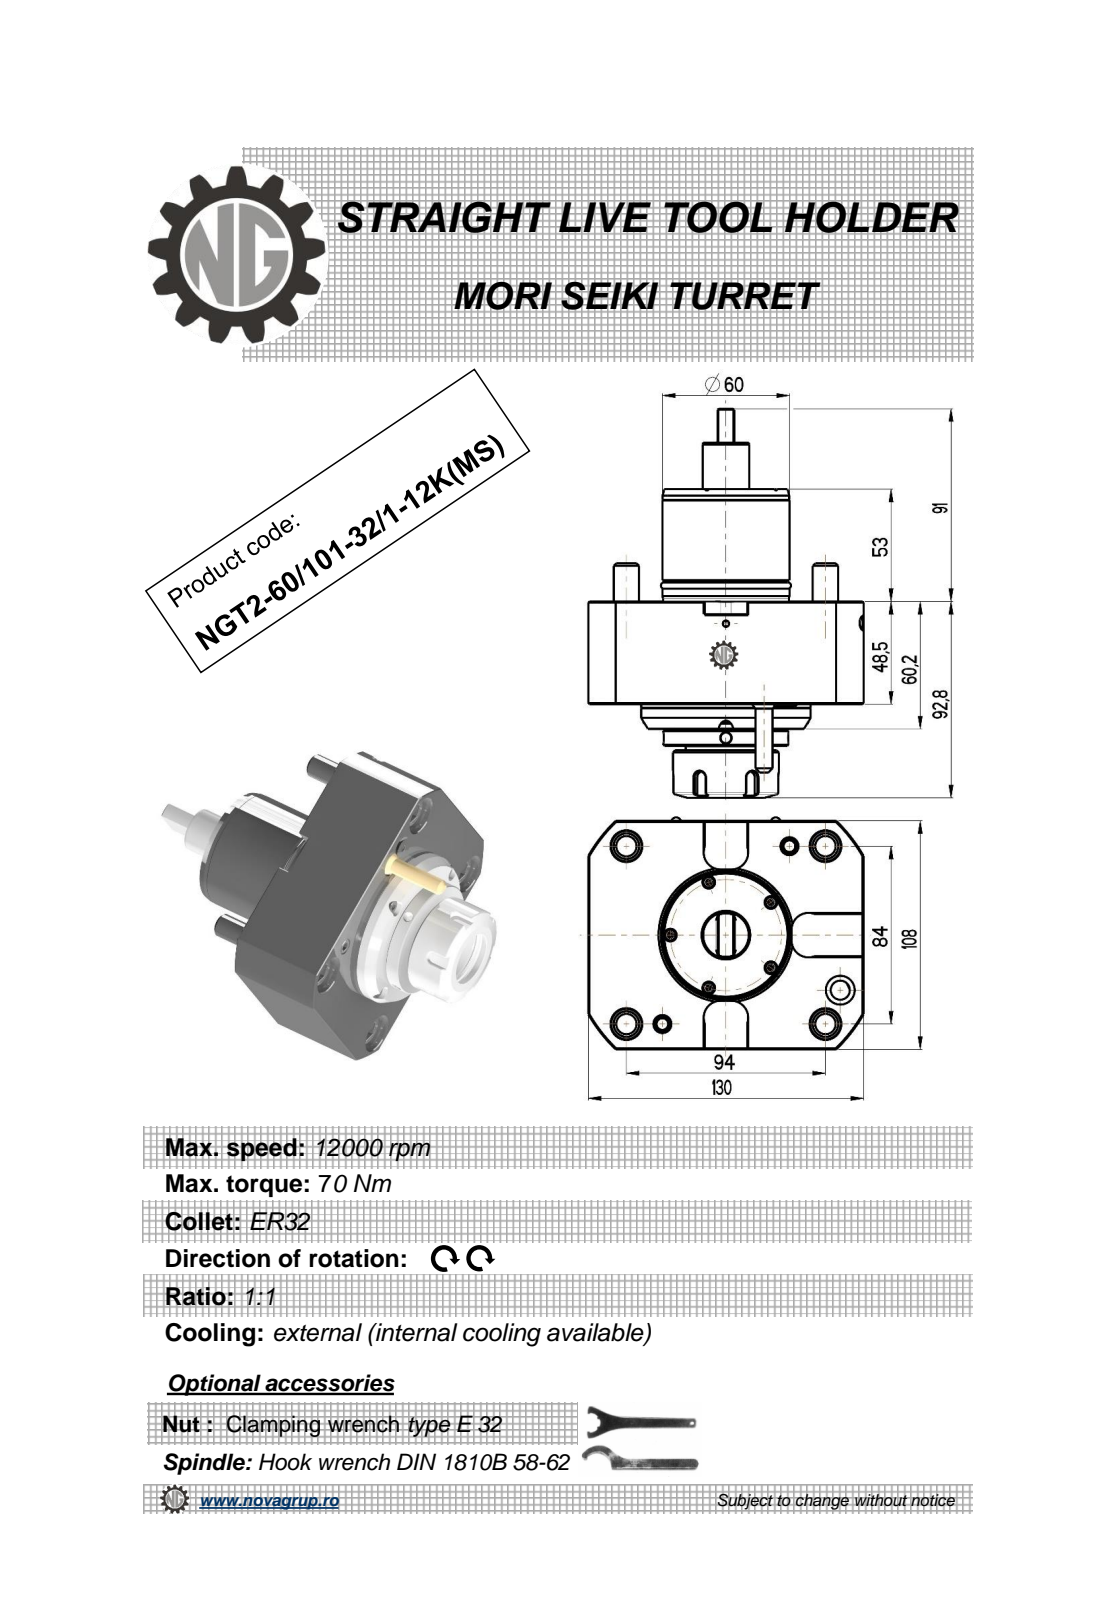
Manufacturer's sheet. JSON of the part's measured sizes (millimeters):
{"part_name": "NGT2_60_101_32_1_MS", "step_written_by": "PRO/ENGINEER BY PARAMETRIC TECHNOLOGY CORPORATION, 2010280 (CONFIG_CONTROL_DESIGN)", "units": "millimeters", "bodies": {"solids": 2, "faces": 267, "planar": 93, "cylindrical": 83, "other": 91}, "overall_size": [183.8, 130, 109.6], "volume_mm3": 934229, "surface_area_mm2": 78764, "round_holes": [[5, 3], [3, 1], [9, 1], [27, 1]], "round_bosses_or_shafts": [[12, 4], [80, 1], [60, 1], [59.8, 1], [59.4, 1], [55.4, 1], [50, 1], [48, 1]], "partial_cylinders_radius": [[0.22, 6], [8, 6], [3, 5], [3.5, 4], [0.8, 2], [10.75, 1], [75, 1]], "face_to_face_distances": [48.5, 108, 130, 60.2, 11.7, 53, 101.5, 113.2, 6, 59], "hole_center_spacings": [39.81, 46.62, 59.93]}
